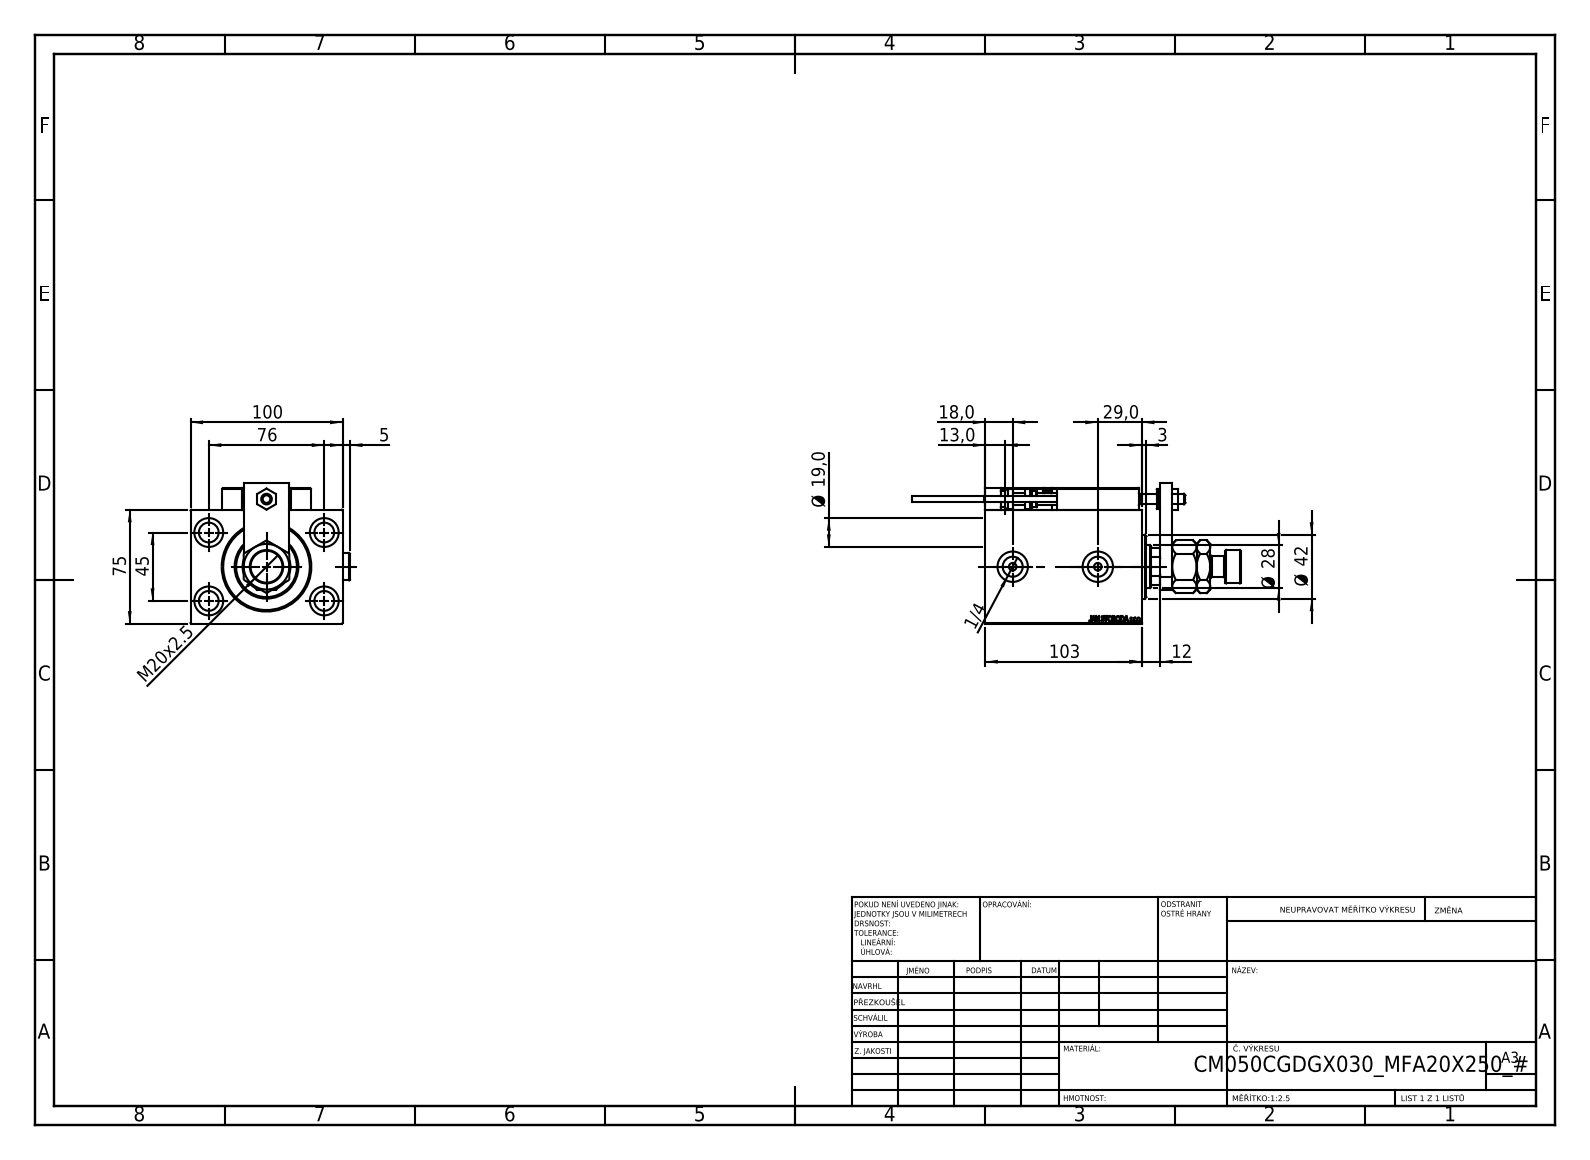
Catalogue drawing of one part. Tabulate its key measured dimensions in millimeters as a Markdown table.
| quantity | value |
| --- | --- |
| part name | V450CM_VC_B; X_Y_MFA; Zatka_OIL_PORT; V450CM_C_VCP (+7 more) |
| STEP written by | SolidWorks 2019 (CONFIG_CONTROL_DESIGN) |
| units | millimeters |
| bodies | 26 solids, 1391 faces (611 planar, 210 cylindrical, 570 other) |
| overall size | 216 × 104.9 × 92.5 |
| volume | 737 676 mm³ |
| surface area | 144 731 mm² |
| round holes (diameter × count) | 8 × 5, 3.2 × 4, 4 × 4, 5 × 4, 13 × 4, 19 × 4, 20 × 3, 13.16 × 2, 7 × 1, 18.5 × 1, 28 × 1, 31.5 × 1 |
| round bosses / shafts (diameter × count) | 18 × 2, 5 × 2, 3.8 × 2, 42 × 1, 22 × 1, 14 × 1, 13 × 1, 11 × 1 |
| partial cylindrical surfaces (radius × count) | 0.3 × 30, 3 × 2, 13.5 × 1 |
| main face-to-face distances | 75, 14, 100, 89, 103, 12, 20, 8, 77, 24 |
| hole center spacings | 44.16, 11.37, 20, 29.59, 29.69, 36.06, 42.19, 43.91 |
